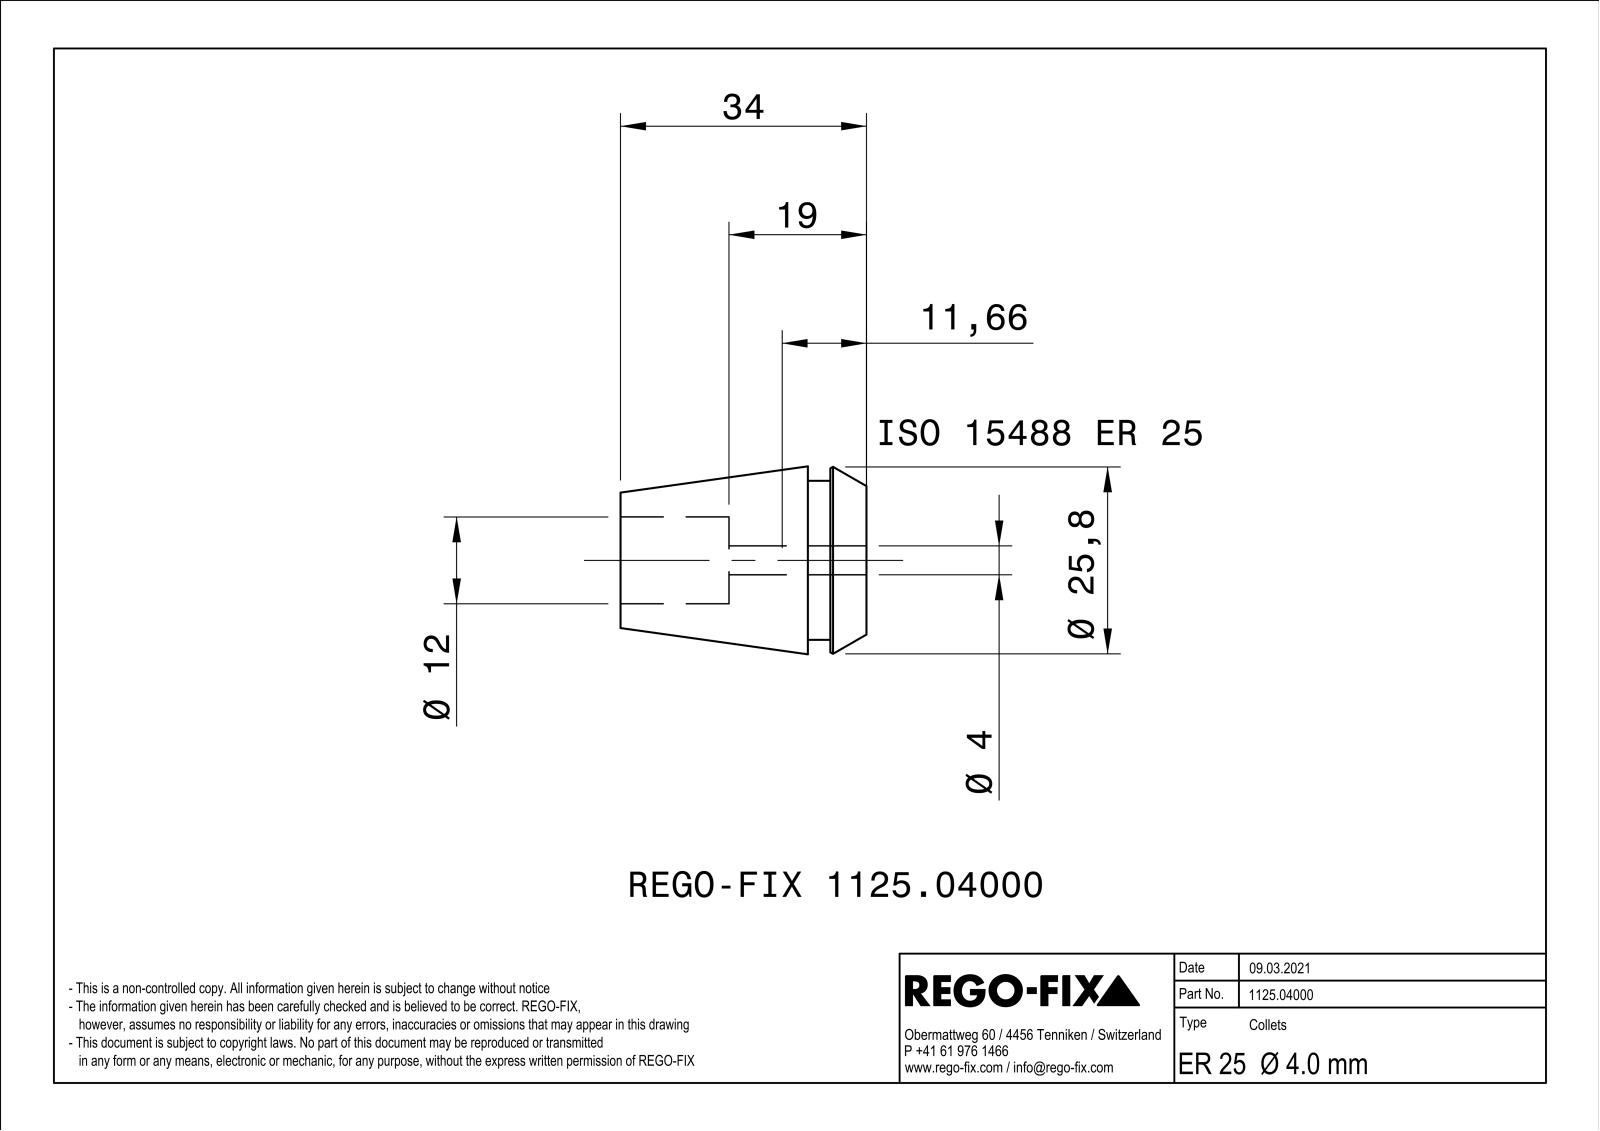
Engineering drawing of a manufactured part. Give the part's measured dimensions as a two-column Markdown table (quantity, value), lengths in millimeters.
| quantity | value |
| --- | --- |
| part name | NOCUT |
| STEP written by | SIEMENS PLM Software Solid Edge ST10 (AUTOMOTIVE_DESIGN) |
| units | millimeters |
| bodies | 1 solid, 272 faces (104 planar, 48 cylindrical, 120 other) |
| overall size | 34 × 25.99 × 25.99 |
| volume | 9 911 mm³ |
| surface area | 9 378 mm² |
| round holes (diameter × count) | 12 × 1 |
| round bosses / shafts (diameter × count) | 22 × 1 |
| partial cylindrical surfaces (radius × count) | 40 × 8, 2 × 1 |
| main face-to-face distances | 0.6, 0.62, 0.58, 8.1, 34, 25.9, 5, 3.1, 29, 19 |
